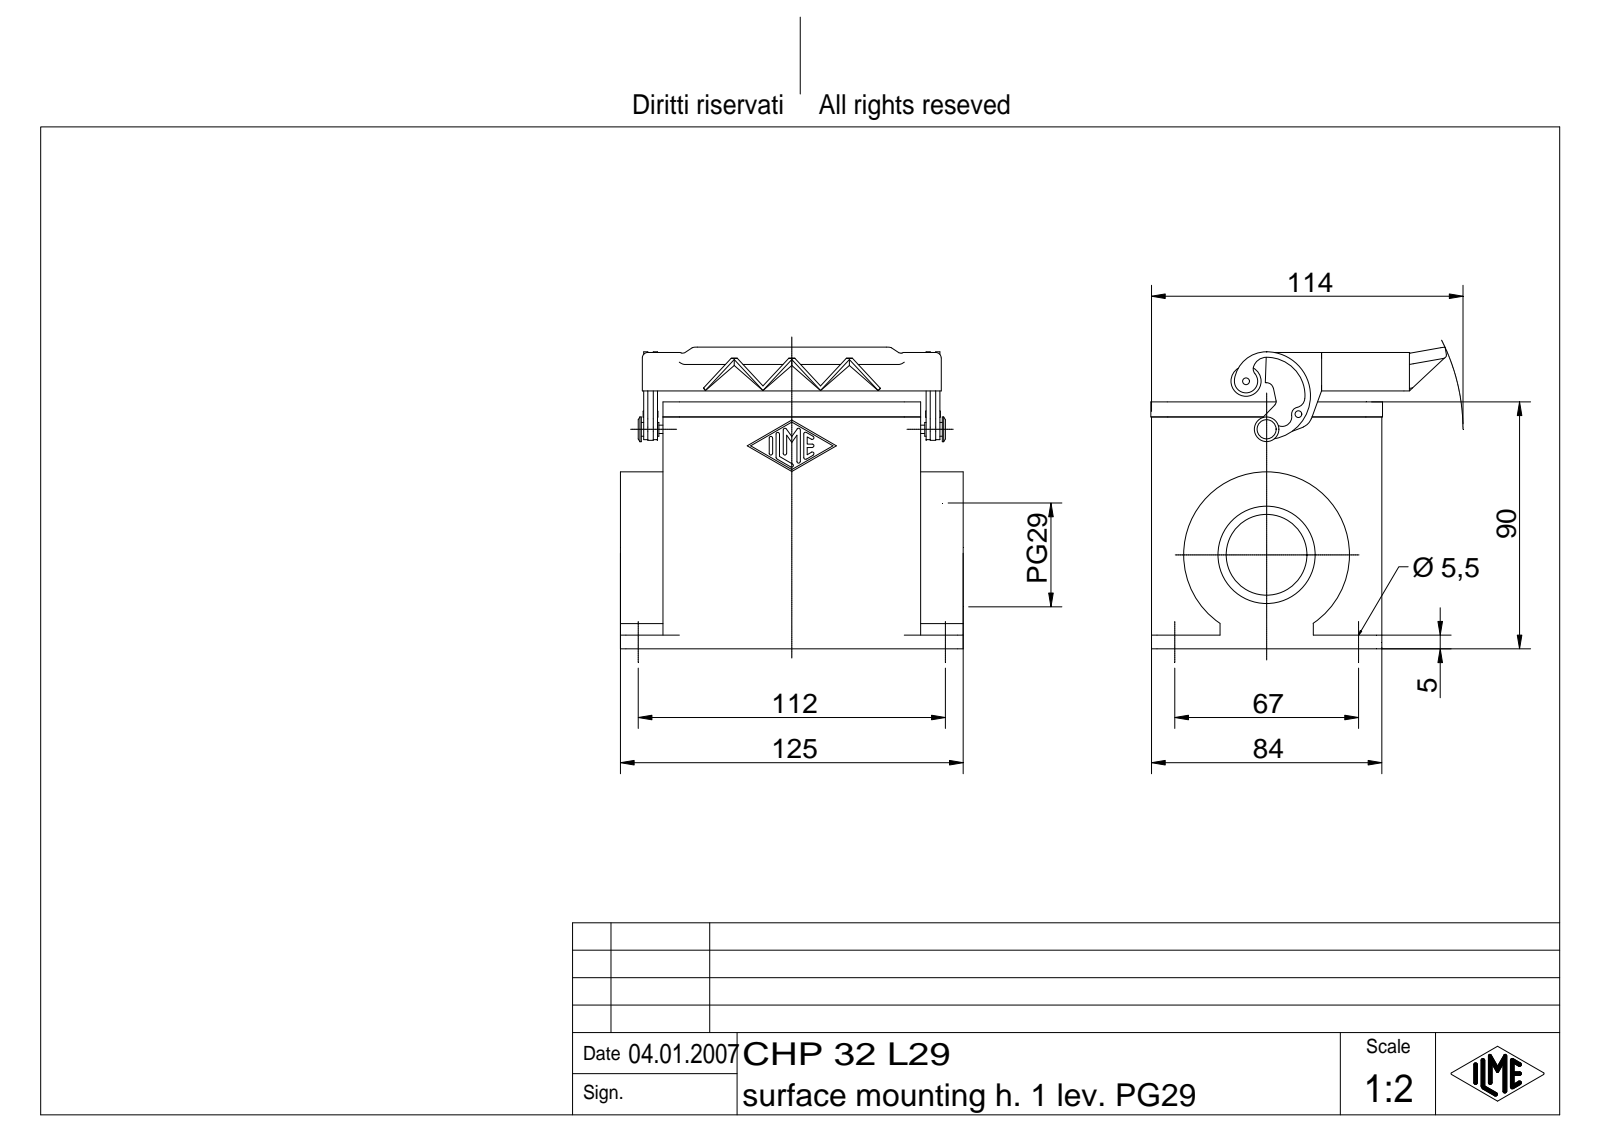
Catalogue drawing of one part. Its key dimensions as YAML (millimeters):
part_name: "CHP 32 L29"
step_written_by: "Autodesk Inventor 7 (AUTOMOTIVE_DESIGN)"
units: millimeters
bodies: {solids: 4, faces: 491, planar: 166, cylindrical: 145, other: 180}
overall_size: [125, 109.98, 107.84]
volume: 279192
surface_area: 105878
round_holes:
  - {diameter: 5.5, count: 4}
  - {diameter: 2, count: 1}
  - {diameter: 29.48, count: 1}
  - {diameter: 35.48, count: 1}
round_bosses_or_shafts:
  - {diameter: 60.5, count: 1}
  - {diameter: 11, count: 1}
  - {diameter: 9, count: 1}
  - {diameter: 5, count: 1}
  - {diameter: 3, count: 1}
  - {diameter: 2.5, count: 1}
partial_cylinders:
  - {radius: 2, count: 16}
  - {radius: 0.62, count: 14}
  - {radius: 1.5, count: 9}
  - {radius: 6, count: 8}
  - {radius: 0.14, count: 4}
  - {radius: 3, count: 4}
  - {radius: 1, count: 3}
  - {radius: 2.5, count: 3}
face_to_face_distances: [3, 81, 84, 4, 11.5, 82.5, 78, 98, 71, 15.5]
hole_center_spacings: [67, 112, 130.51, 52.56]
